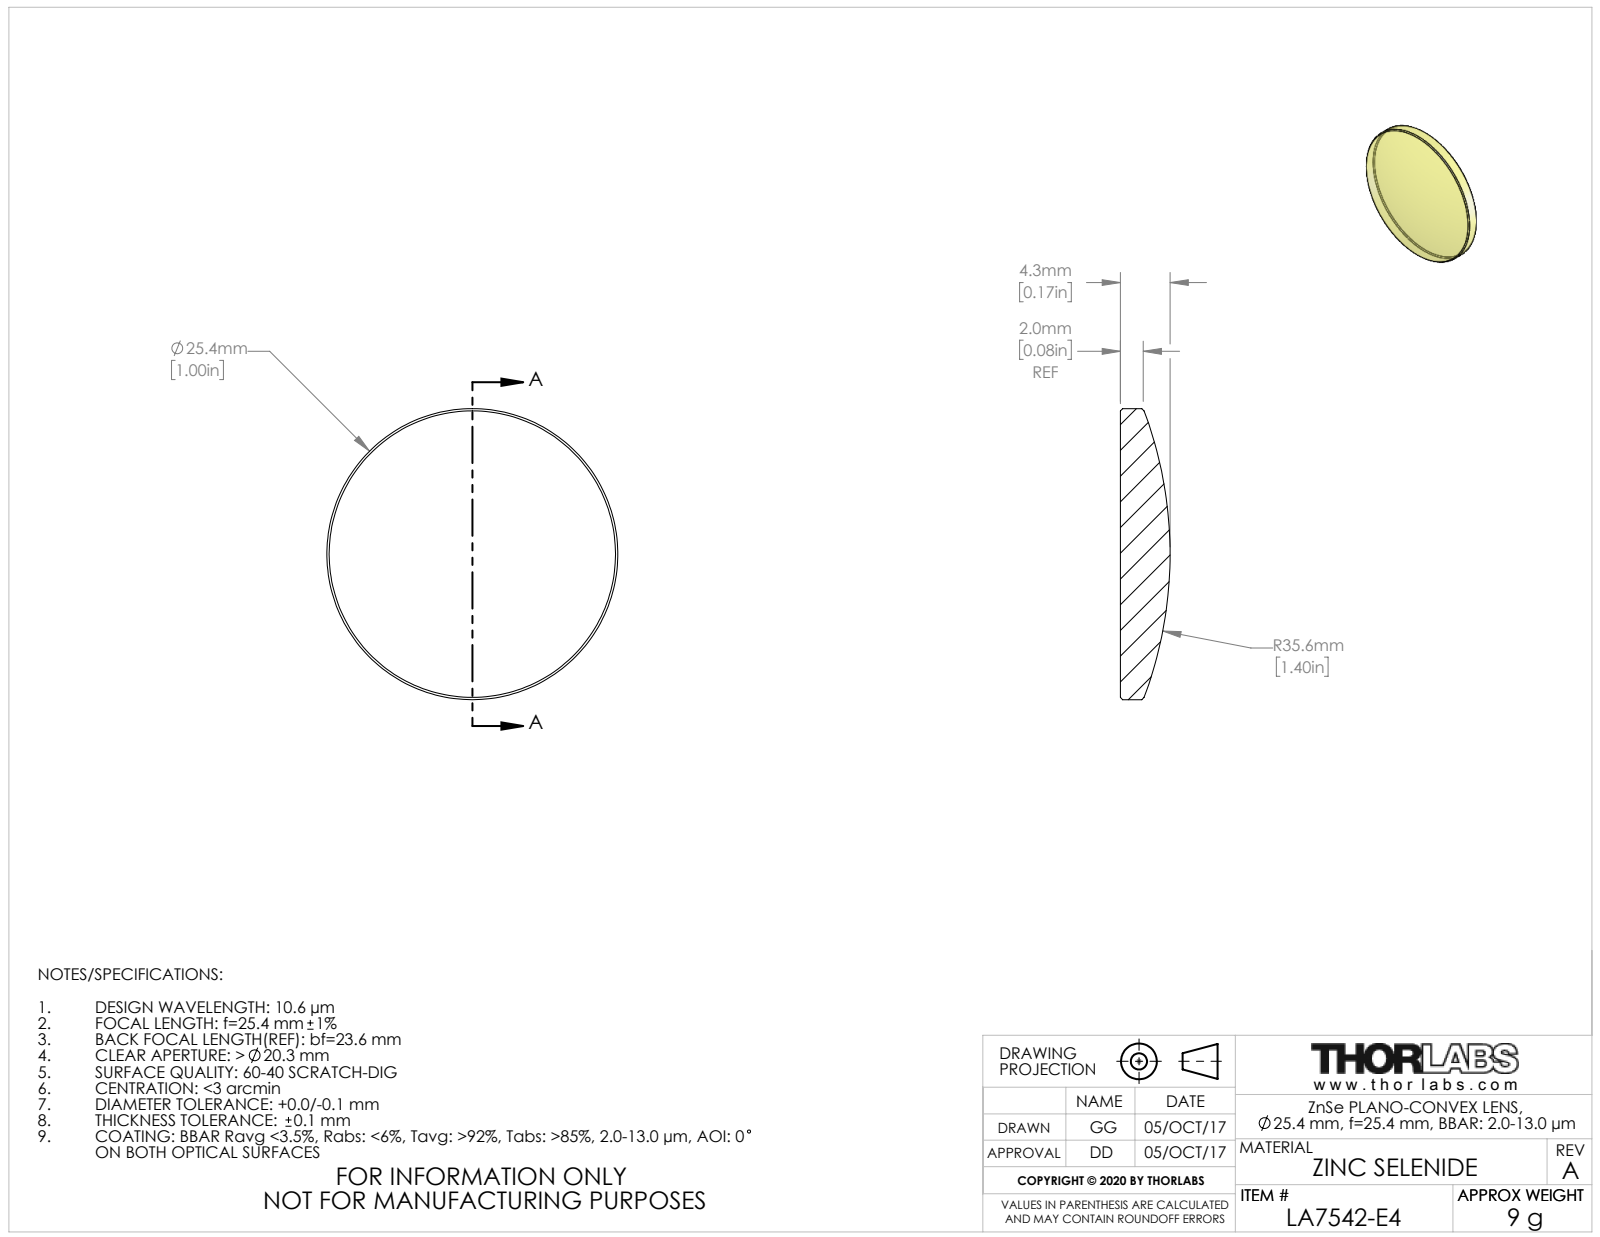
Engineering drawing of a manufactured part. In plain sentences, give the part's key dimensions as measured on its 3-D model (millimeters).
The part is named "TTN098089-E0W". Its 3-D file was written by "SolidWorks 2018 (CONFIG_CONTROL_DESIGN)". It is 1 solid with 9 faces: 1 planar, 2 cylindrical and 6 other. Overall it measures 25.4 by 25.4 by 4.34 millimeters. Its volume is 1 610 cubic millimeters and its surface area 1 176 square millimeters. Round bosses or shafts: 1 of diameter 25.4.
